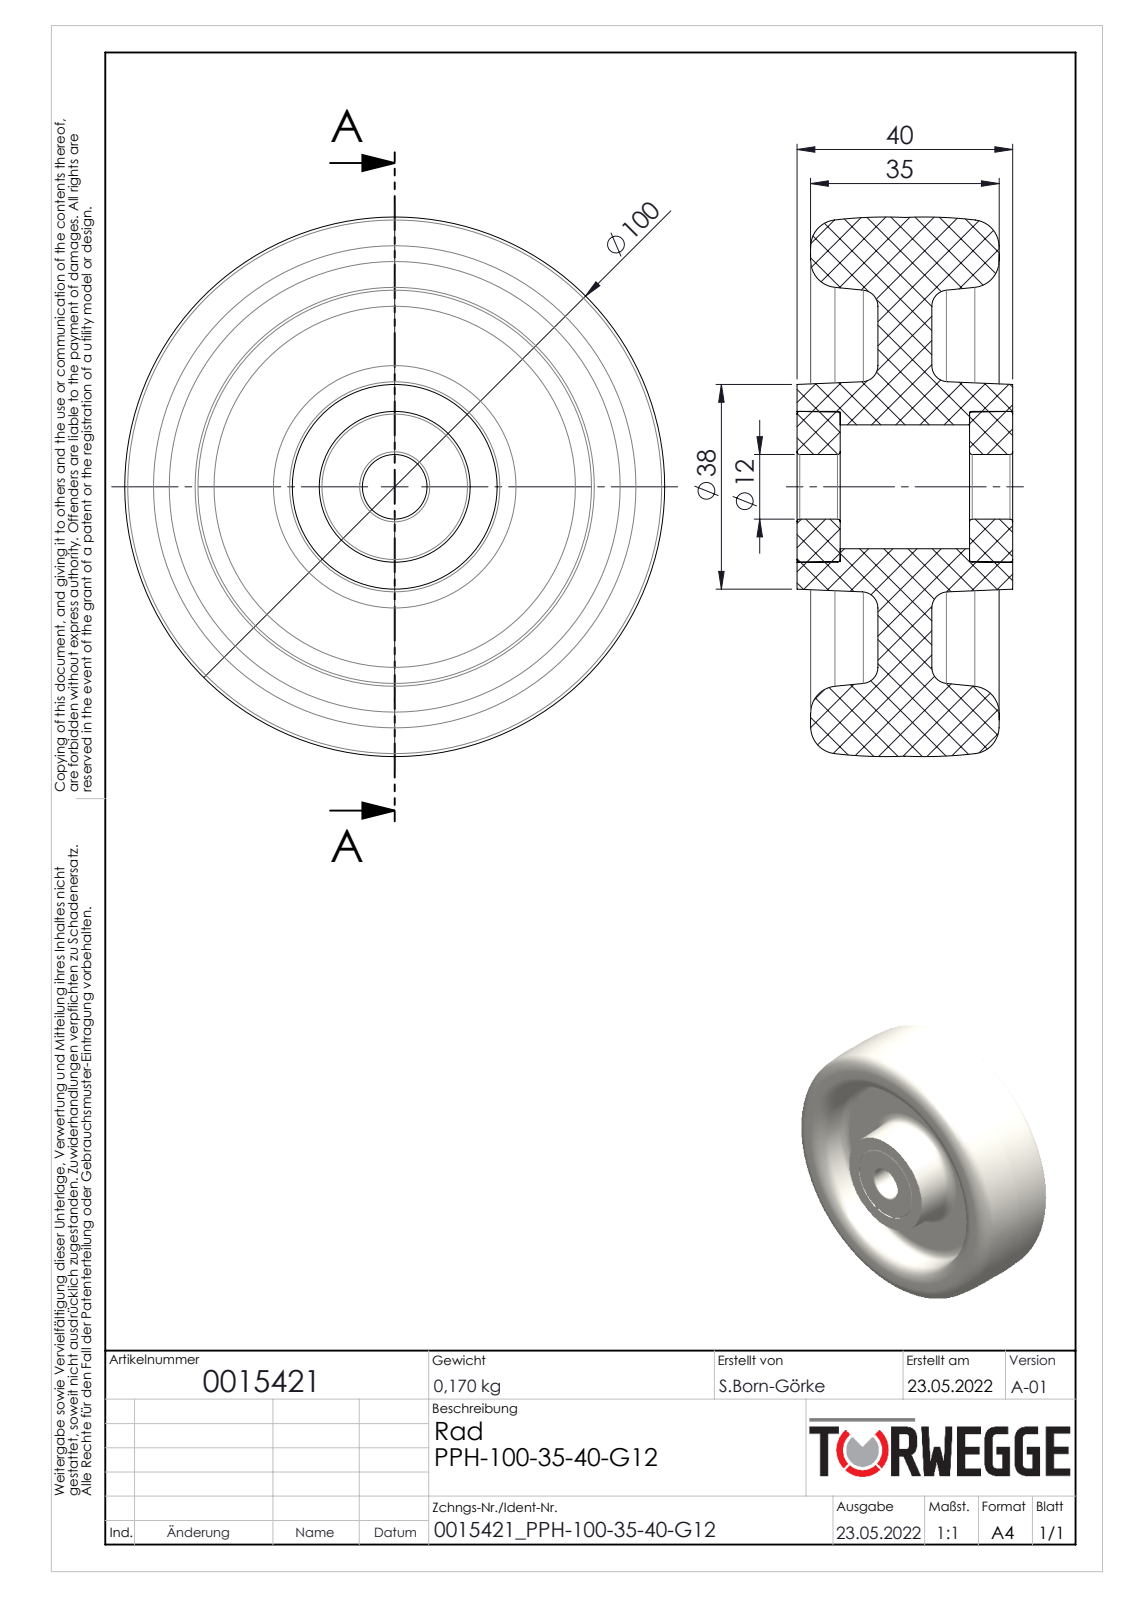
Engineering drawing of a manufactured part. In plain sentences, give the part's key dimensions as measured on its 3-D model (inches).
The part is named "0015421". Its 3-D file was written by "SolidWorks 2020 (AUTOMOTIVE_DESIGN)". It is 3 solids with 72 faces: 10 planar, 10 cylindrical and 52 other. Overall it measures 3.944 by 3.944 by 1.575 inches. Its volume is 11.33 cubic inches and its surface area 59.55 square inches. Round holes: 1 of diameter 0.472, 1 of diameter 0.906. Round bosses or shafts: 1 of diameter 1.102. The main face-to-face distances are 0.394, 0.591, 0.984, 0.315, 1.26, 0.276, 0.669, 1.575, 0.945.
